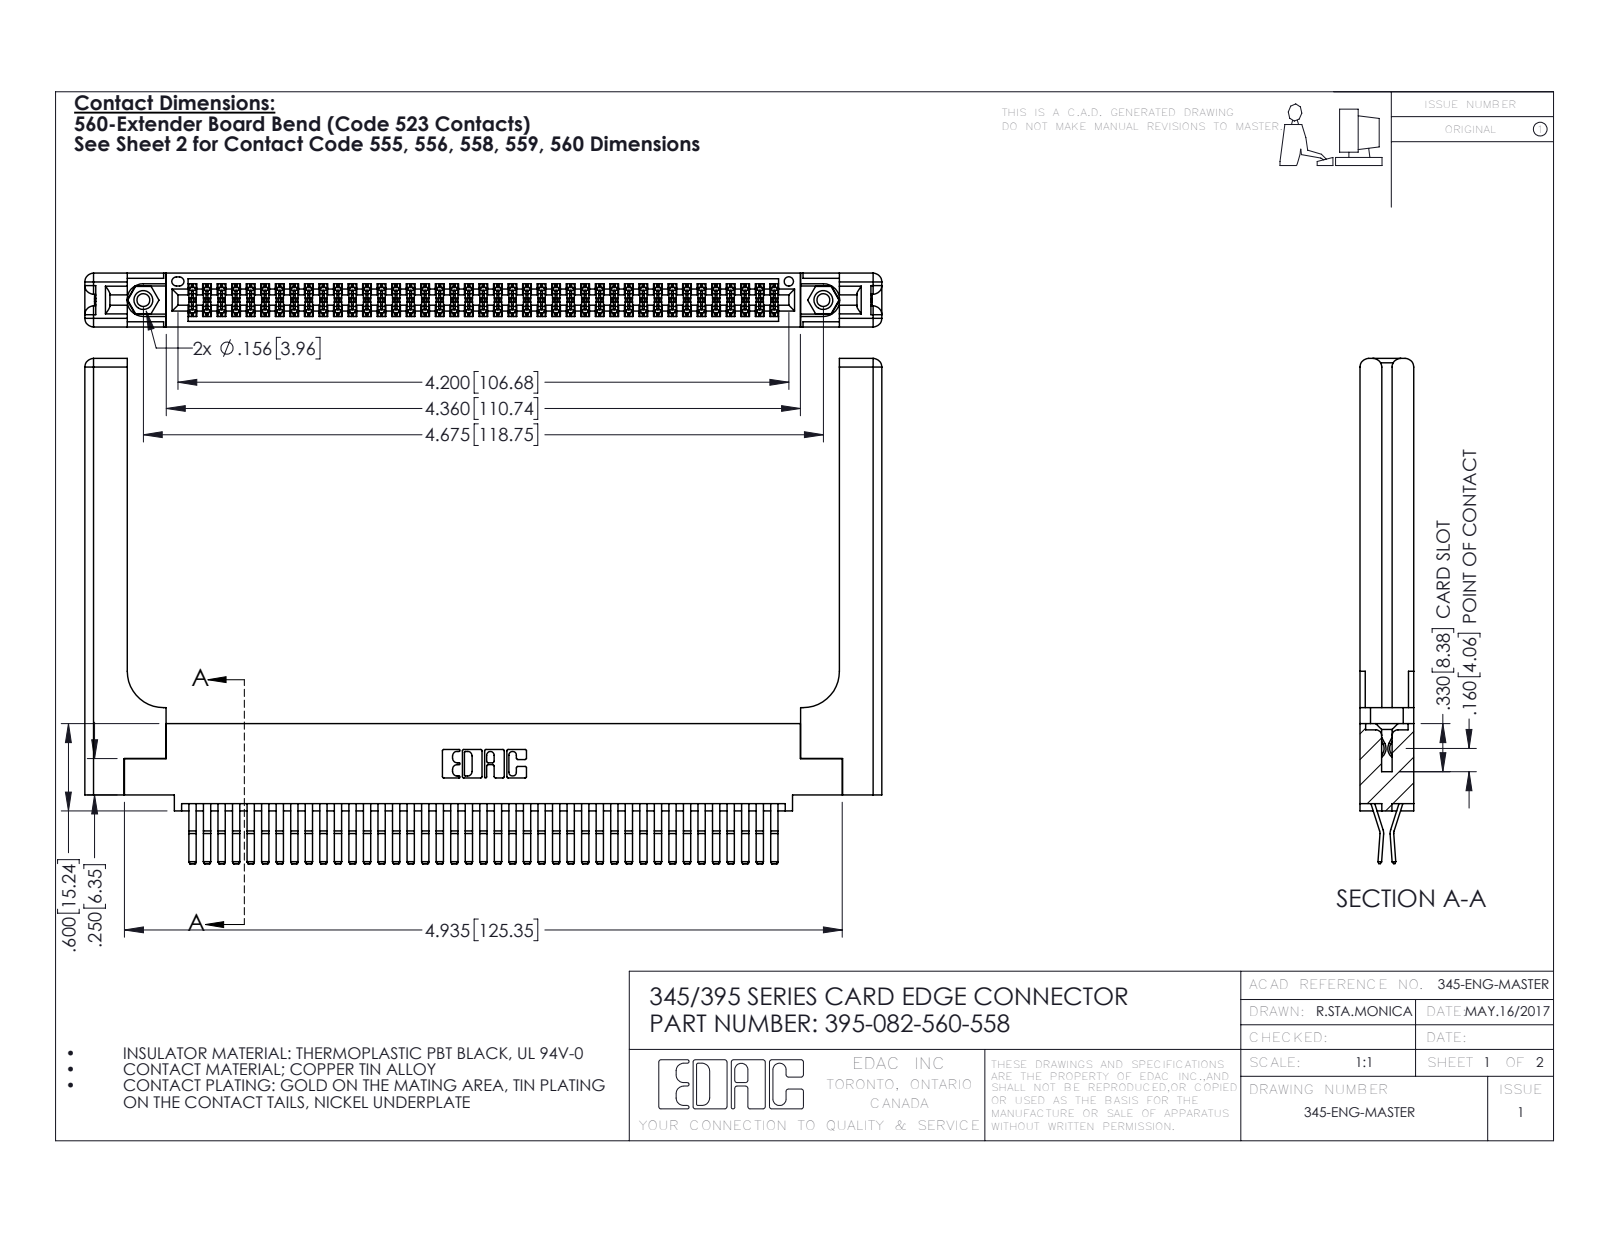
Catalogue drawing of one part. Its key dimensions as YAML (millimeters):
part_name: "345 Part_0.110 Offset - 0.156 Dia-TH; 345-292-001_560 Tail; 395-082-560-558; 345-250-001_345-250-001-102 (+1 more)"
step_written_by: "SolidWorks 2016 (CONFIG_CONTROL_DESIGN)"
units: millimeters
bodies: {solids: 87, faces: 4650, planar: 2938, cylindrical: 1652, other: 60}
overall_size: [139.2, 88.2, 9.4]
volume: 22450
surface_area: 27170
round_holes:
  - {diameter: 2.3, count: 2}
  - {diameter: 3.2, count: 2}
  - {diameter: 4, count: 2}
  - {diameter: 1.6, count: 1}
round_bosses_or_shafts:
  - {diameter: 3.9, count: 2}
partial_cylinders:
  - {radius: 0.2, count: 124}
  - {radius: 0.3, count: 22}
  - {radius: 1.5, count: 16}
  - {radius: 0.2, count: 6}
  - {radius: 0.8, count: 6}
  - {radius: 0.7, count: 3}
  - {radius: 0.3, count: 2}
  - {radius: 0.4, count: 2}
face_to_face_distances: [1.8, 9.4, 7.6, 0.6, 5.1, 2.5, 6.9, 5.7, 3.8, 3.8]
hole_center_spacings: [6.9, 112.8, 118.7]
